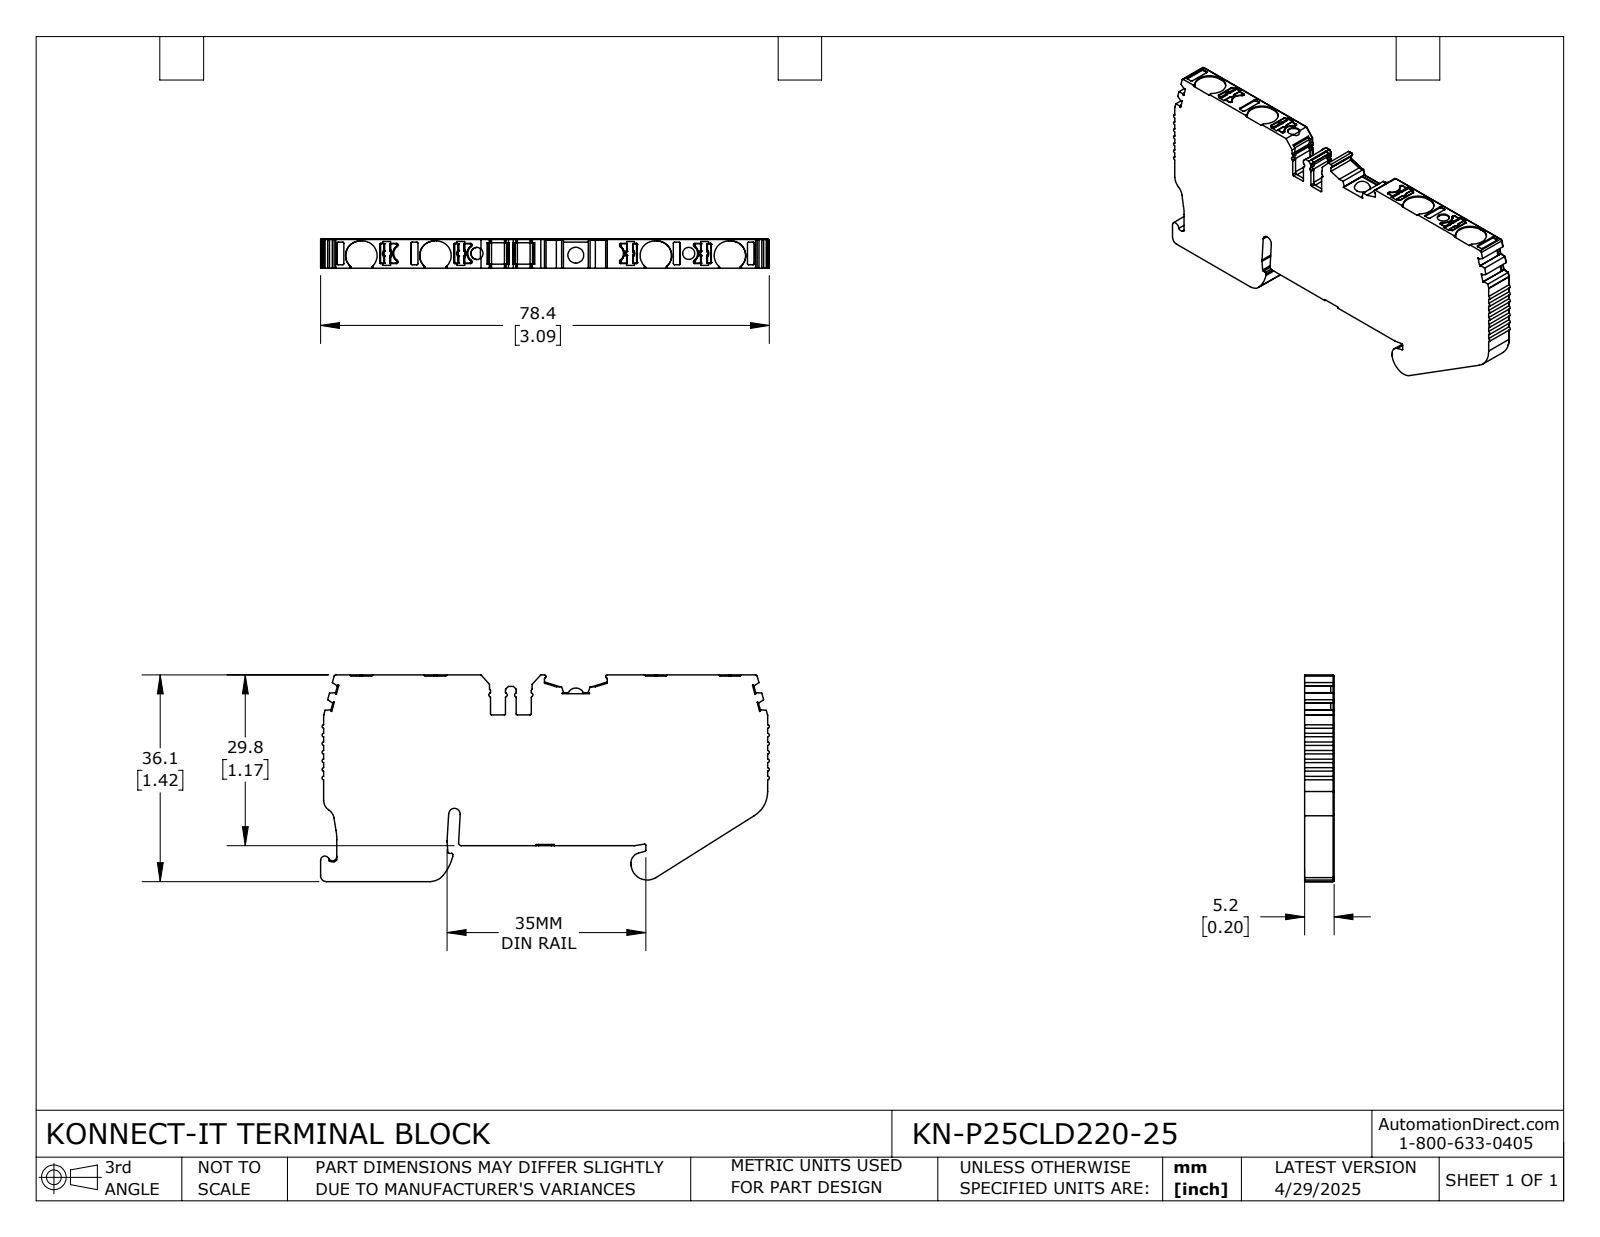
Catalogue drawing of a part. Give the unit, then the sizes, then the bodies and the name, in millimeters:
Units: millimetres
Overall size (bounding box): 78.36 × 36.07 × 5.15
Round holes (diameter × count): ⌀2.1 ×2
Partial cylindrical surfaces — rounded edges, fillets, slot ends (radius × count): R0.2 ×78, R0.3 ×39, R0.1 ×21, R0.5 ×18, R0.15 ×16, R0.4 ×9, R2.55 ×8, R1.5 ×4
Main face-to-face distances: 5.15, 29.61, 29.81, 6.26, 35.87, 36.07, 77.52, 1.2, 5, 4.5
Hole centre spacings: 36.98
Volume: 11 975 mm³ · Surface area: 6 221 mm²
Bodies: 1 solid, 740 faces (381 planar, 291 cylindrical, 68 other)
Part name (STEP PRODUCT): KN-P25CLD220-25
STEP written by: SolidWorks 2024 (CONFIG_CONTROL_DESIGN)
